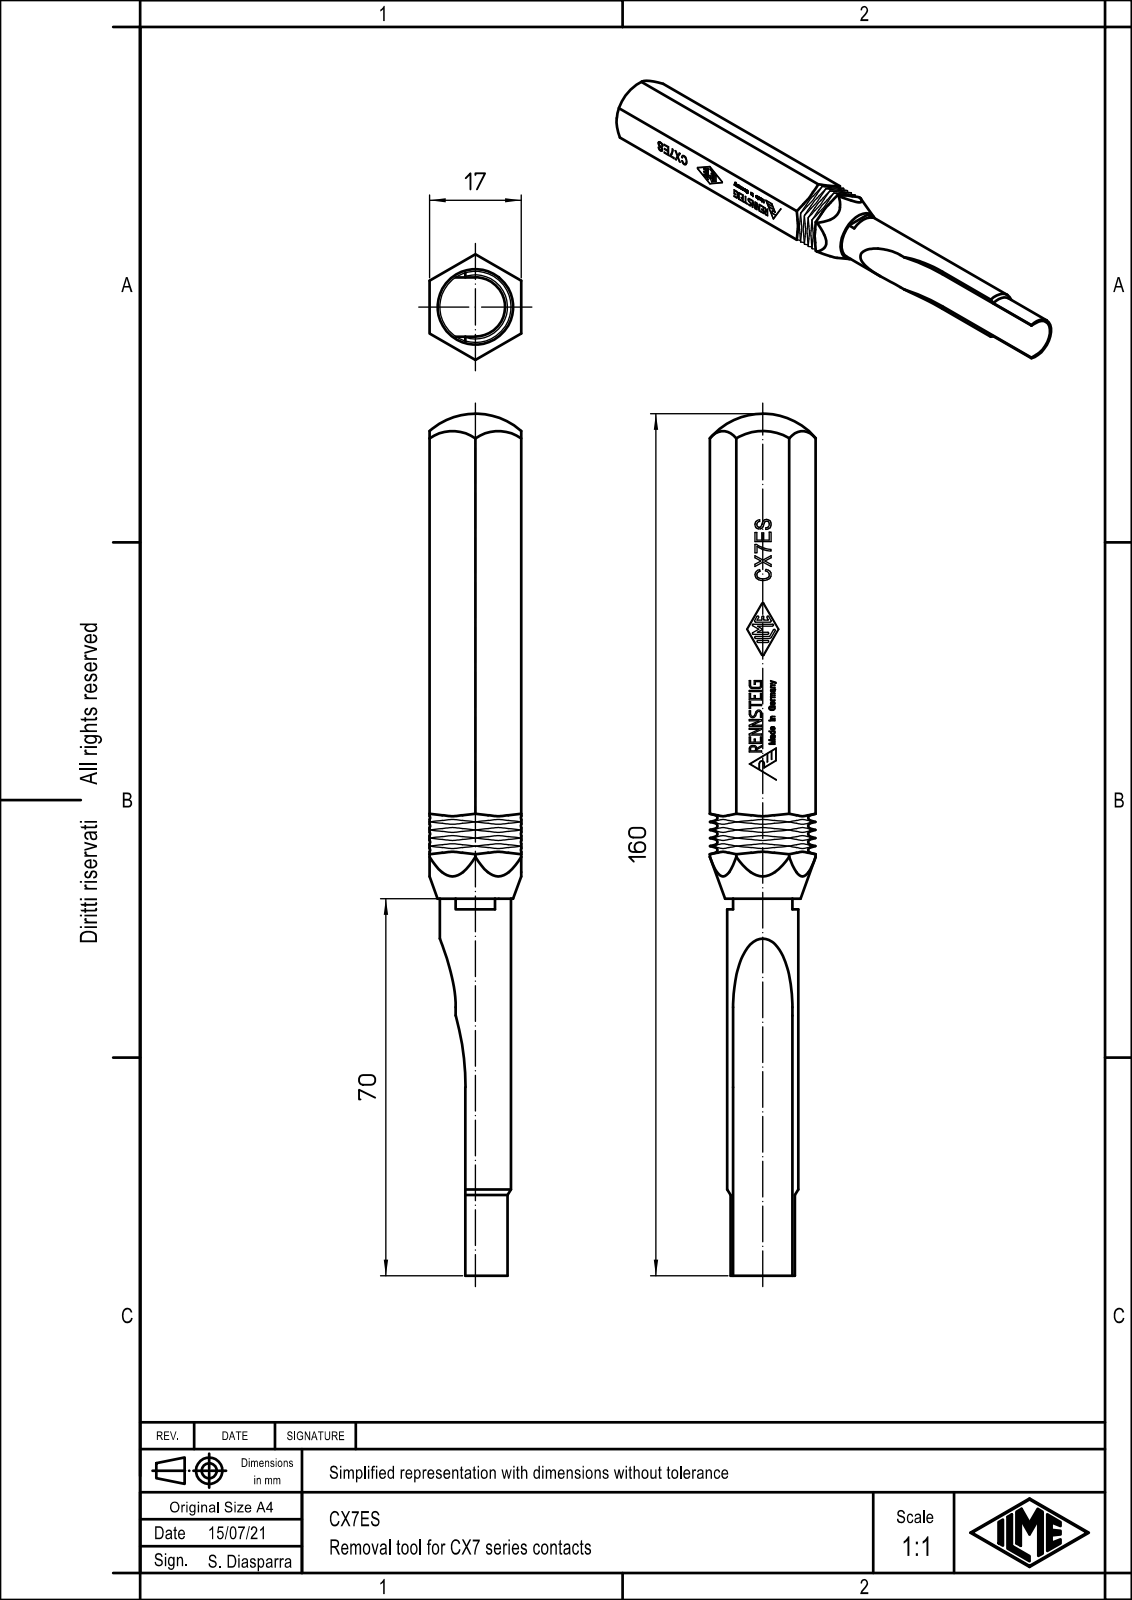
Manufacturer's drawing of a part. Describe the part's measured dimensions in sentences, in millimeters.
The part is named "CX7ES". Its 3-D file was written by "Creo Elements/Direct Modeling 20.1B 02-Apr-2019 (C) Parametric Technology GmbH (AUTOMOTIVE_DESIGN)". It is 1 solid with 170 faces: 88 planar, 6 cylindrical and 76 other. Overall it measures 160 by 19.63 by 17 millimeters. Its volume is 25 131 cubic millimeters and its surface area 8 717 square millimeters. Round bosses or shafts: 1 of diameter 13.2. Partial cylindrical surfaces (rounded edges, fillets, slot ends): 1 of radius 5.5, 1 of radius 5.95, 1 of radius 50. The main face-to-face distances are 17, 11, 6.65, 10.35, 2, 70, 68.
